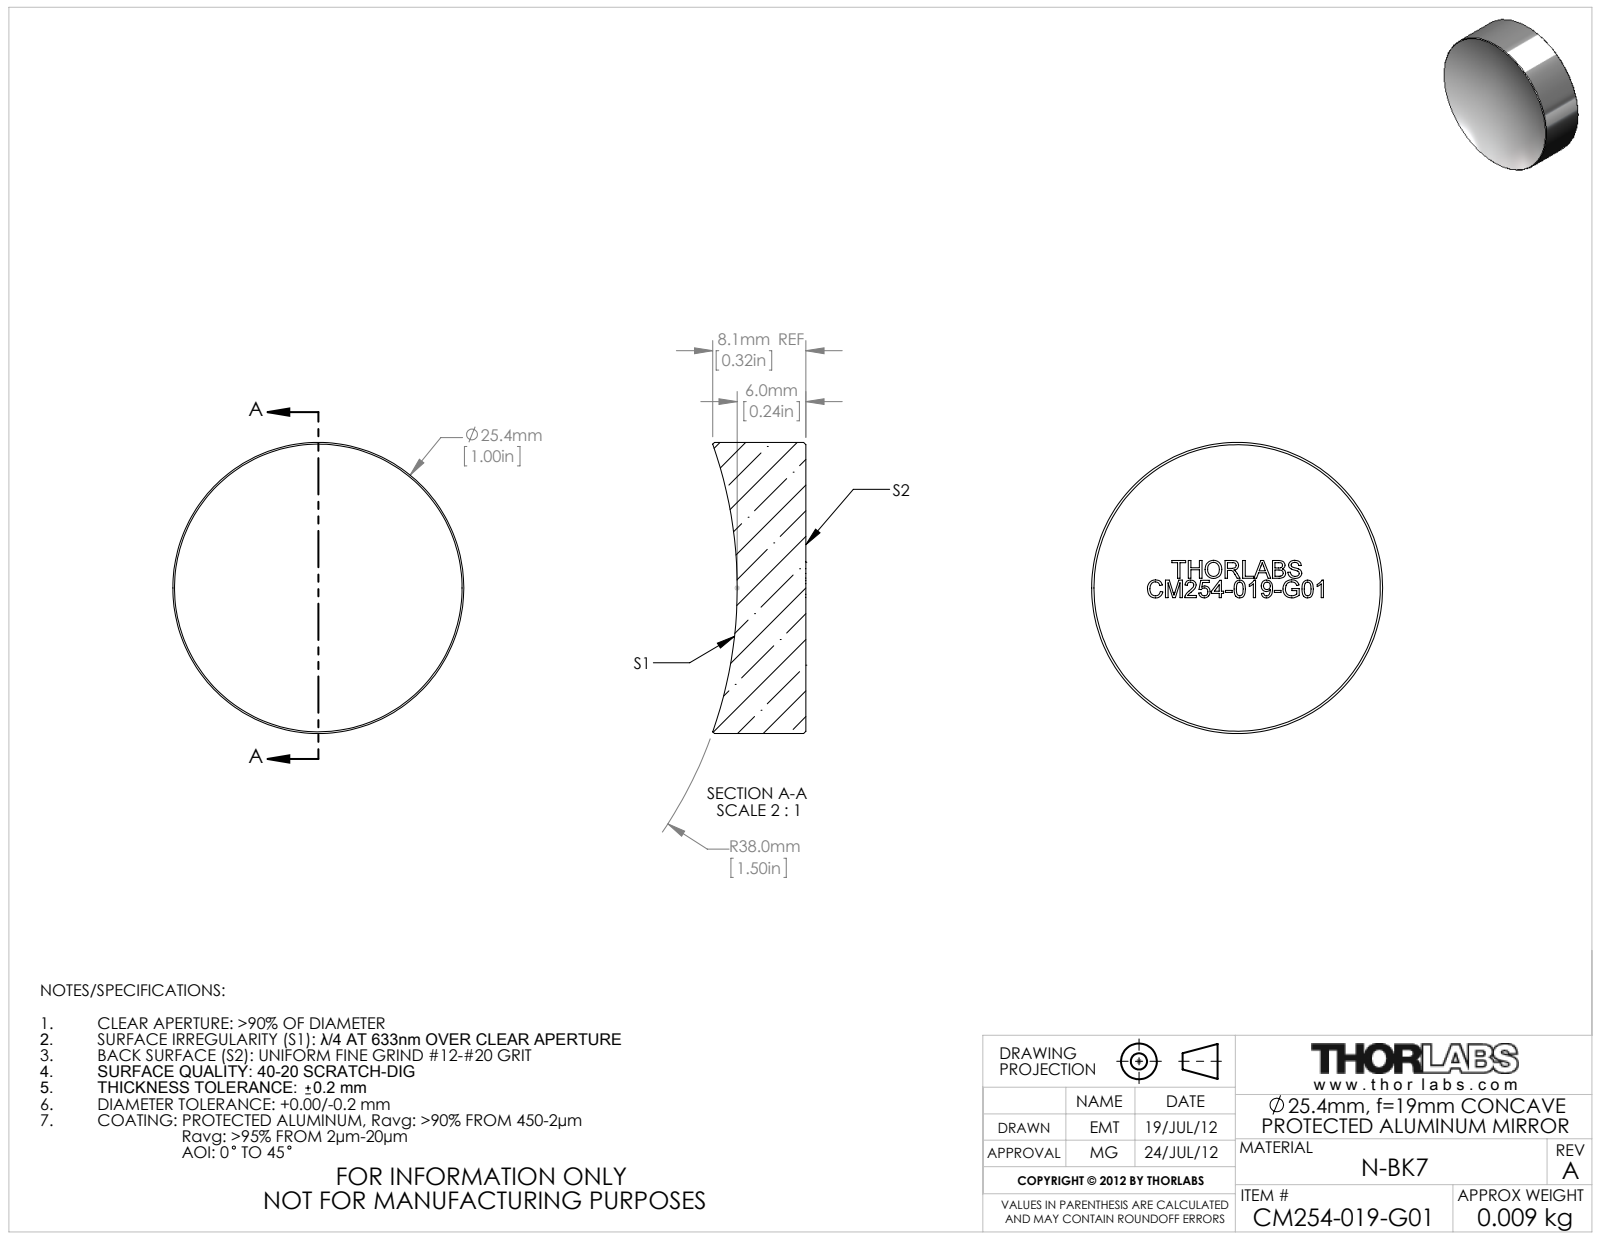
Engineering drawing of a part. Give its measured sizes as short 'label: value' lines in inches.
name: 24630-E0W
written by: SolidWorks 2011 (CONFIG_CONTROL_DESIGN)
unit: in
bodies: 0 solids, 39 faces (31 planar, 2 cylindrical, 6 other)
size: 1 × 1 × 0.32
bosses: 1× ⌀1
